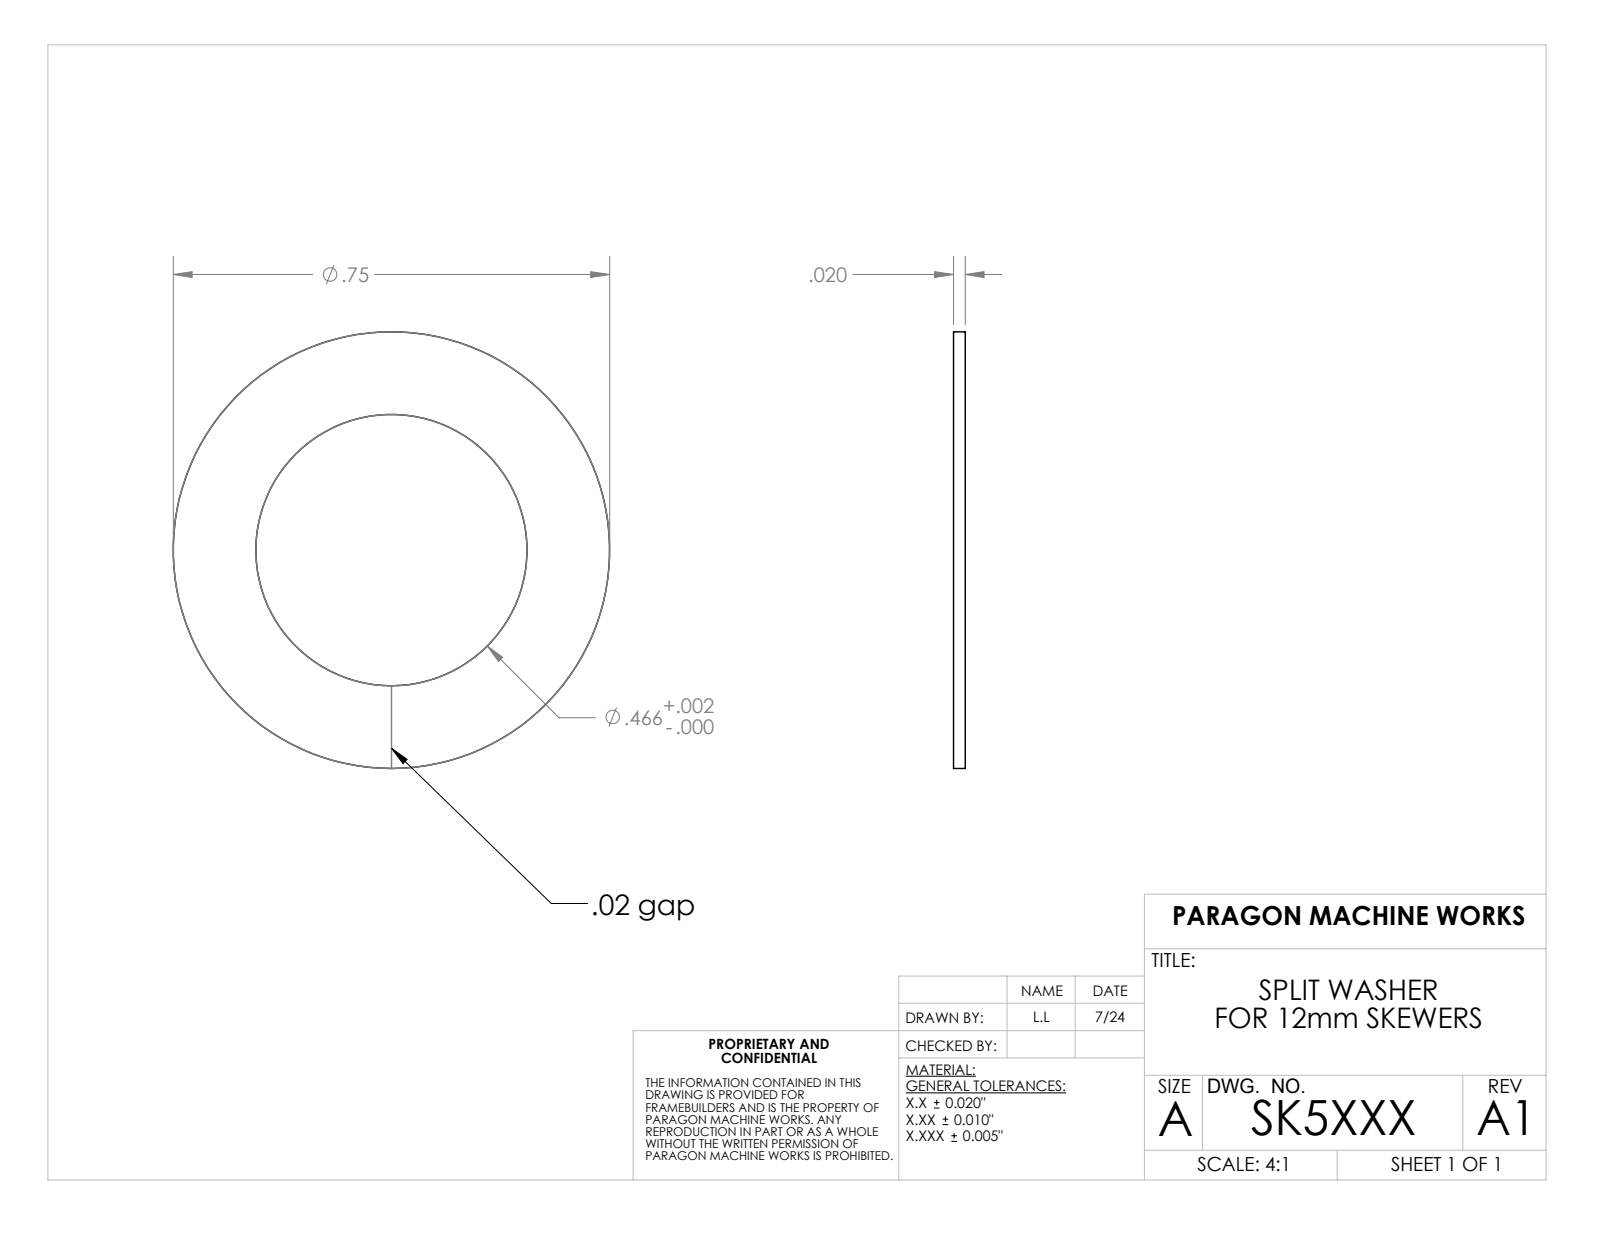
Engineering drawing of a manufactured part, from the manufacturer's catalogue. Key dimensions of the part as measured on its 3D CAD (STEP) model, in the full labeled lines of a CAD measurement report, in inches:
Part name (STEP PRODUCT): SK5001
STEP written by: SolidWorks 2023 (AUTOMOTIVE_DESIGN)
Units: inches
Bodies: 1 solid, 8 faces (4 planar, 4 cylindrical, 0 other)
Overall size (bounding box): 0.75 × 0.75 × 0.02
Volume: 0.005 in³ · Surface area: 0.622 in²
Round holes (diameter × count): ⌀0.466 ×1
Round bosses / shafts (diameter × count): ⌀0.75 ×1
Main face-to-face distances: 0.02
